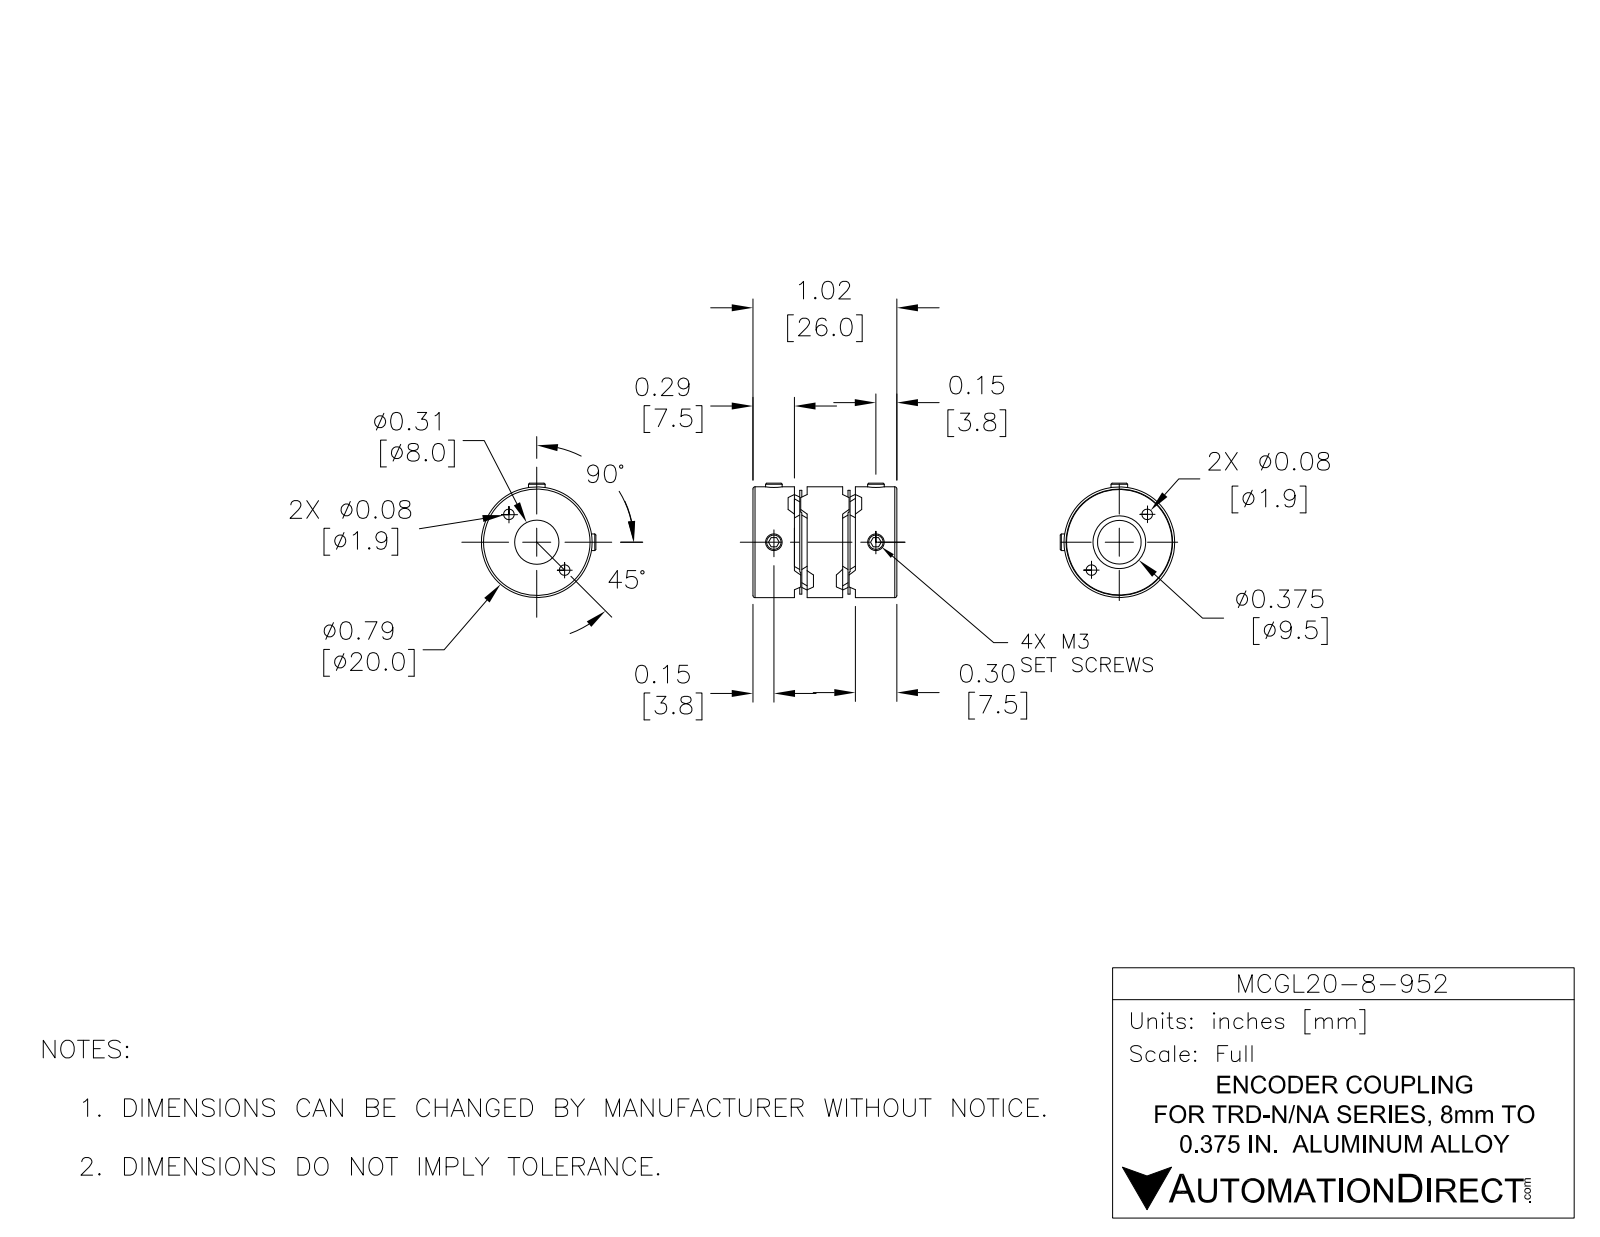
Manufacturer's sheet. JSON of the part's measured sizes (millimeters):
{"part_name": "MCGL20-8-952", "step_written_by": "SolidWorks 2016 (AUTOMOTIVE_DESIGN)", "units": "millimeters", "bodies": {"solids": 1, "faces": 158, "planar": 86, "cylindrical": 36, "other": 36}, "overall_size": [26, 20, 20], "volume_mm3": 5135, "surface_area_mm2": 4617, "round_holes": [[3, 6], [8, 1], [9, 1], [9.53, 1]], "round_bosses_or_shafts": [[20, 1]], "face_to_face_distances": [7.4, 1.4, 2.2, 0.8, 6, 5.2, 17.1, 8.9, 9.7, 16.3], "hole_center_spacings": [7.3, 18.6, 14.6]}
